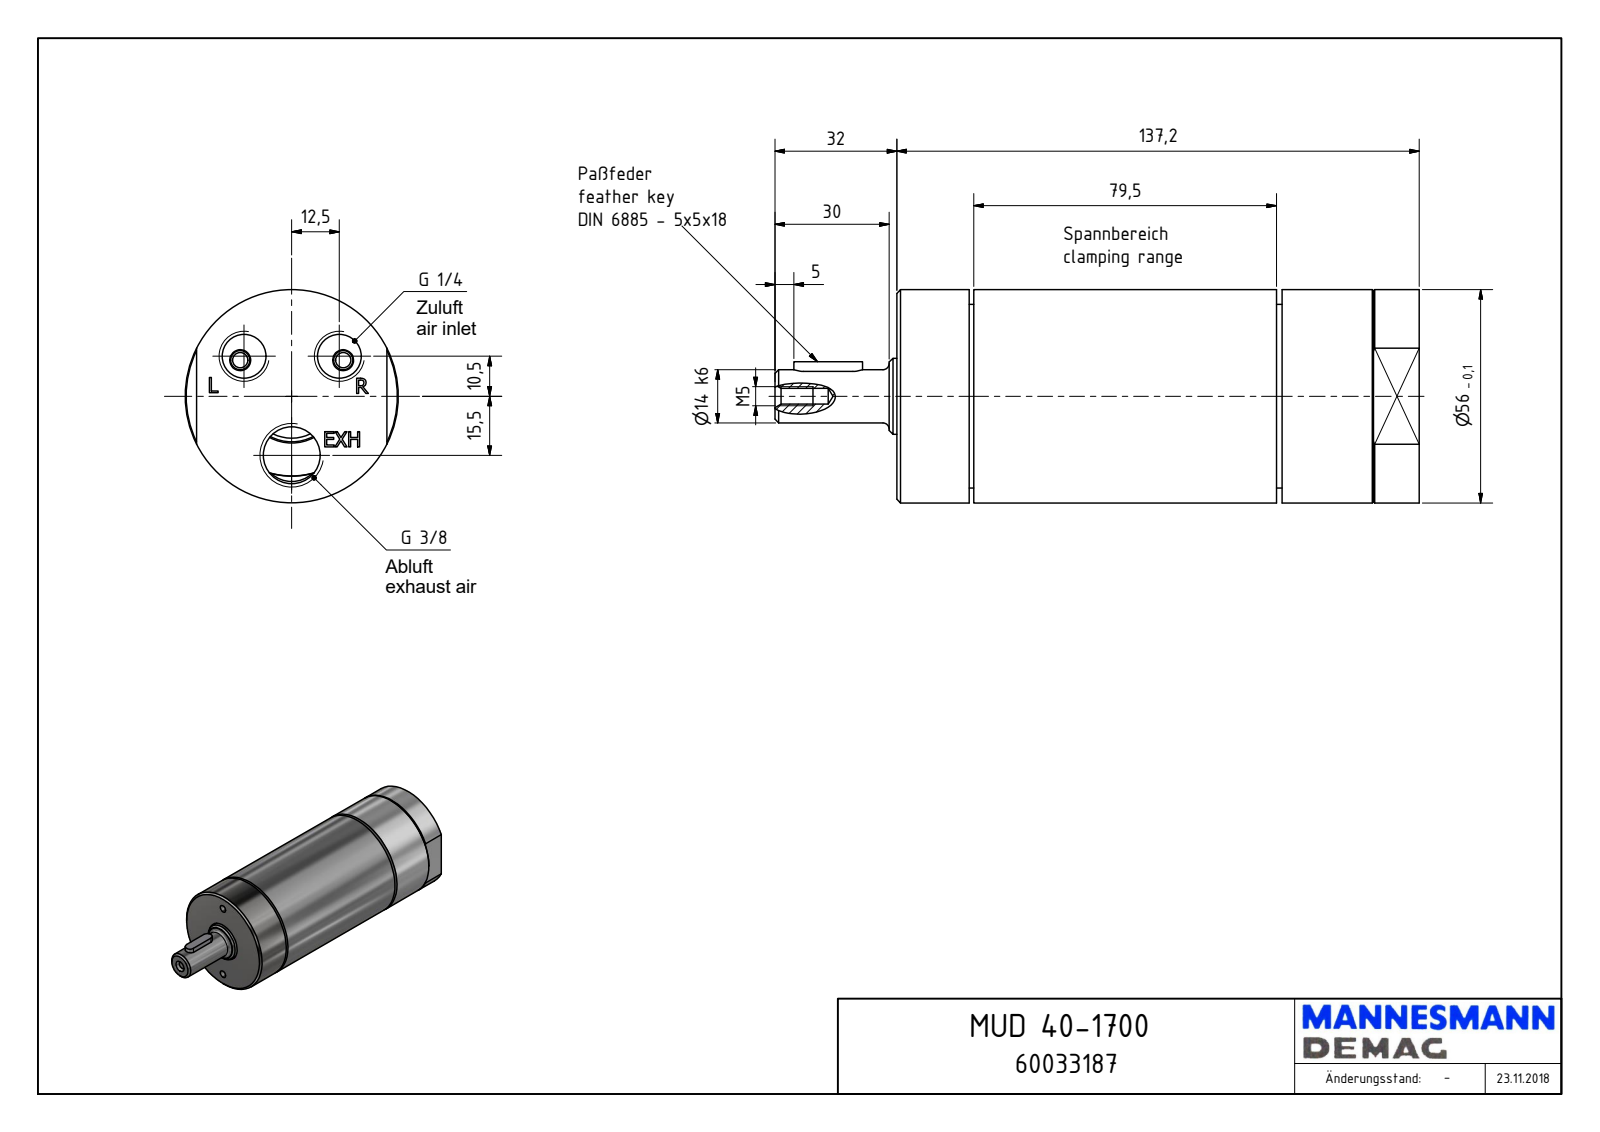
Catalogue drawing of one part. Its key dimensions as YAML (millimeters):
part_name: "MUD 40-1700_60033187"
step_written_by: "Autodesk Inventor 2018 (AUTOMOTIVE_DESIGN)"
units: millimeters
bodies: {solids: 1, faces: 167, planar: 93, cylindrical: 31, other: 43}
overall_size: [169.2, 56, 56]
volume: 336247
surface_area: 36891
round_holes:
  - {diameter: 4, count: 2}
  - {diameter: 11.45, count: 2}
  - {diameter: 4.13, count: 1}
  - {diameter: 14.95, count: 1}
  - {diameter: 21, count: 1}
  - {diameter: 21.25, count: 1}
  - {diameter: 23.54, count: 1}
  - {diameter: 26, count: 1}
  - {diameter: 48.38, count: 1}
round_bosses_or_shafts:
  - {diameter: 56, count: 1}
  - {diameter: 48.18, count: 1}
  - {diameter: 19.95, count: 1}
  - {diameter: 14, count: 1}
partial_cylinders:
  - {radius: 2.5, count: 2}
  - {radius: 6, count: 2}
  - {radius: 21.78, count: 1}
  - {radius: 23, count: 1}
face_to_face_distances: [137.2, 20.2, 117, 99.7, 79.5, 37.5, 1.5, 19, 101.2, 1.2]
hole_center_spacings: [16.32, 21, 28.85, 33.89, 5.5, 15.5, 25, 36.5]
